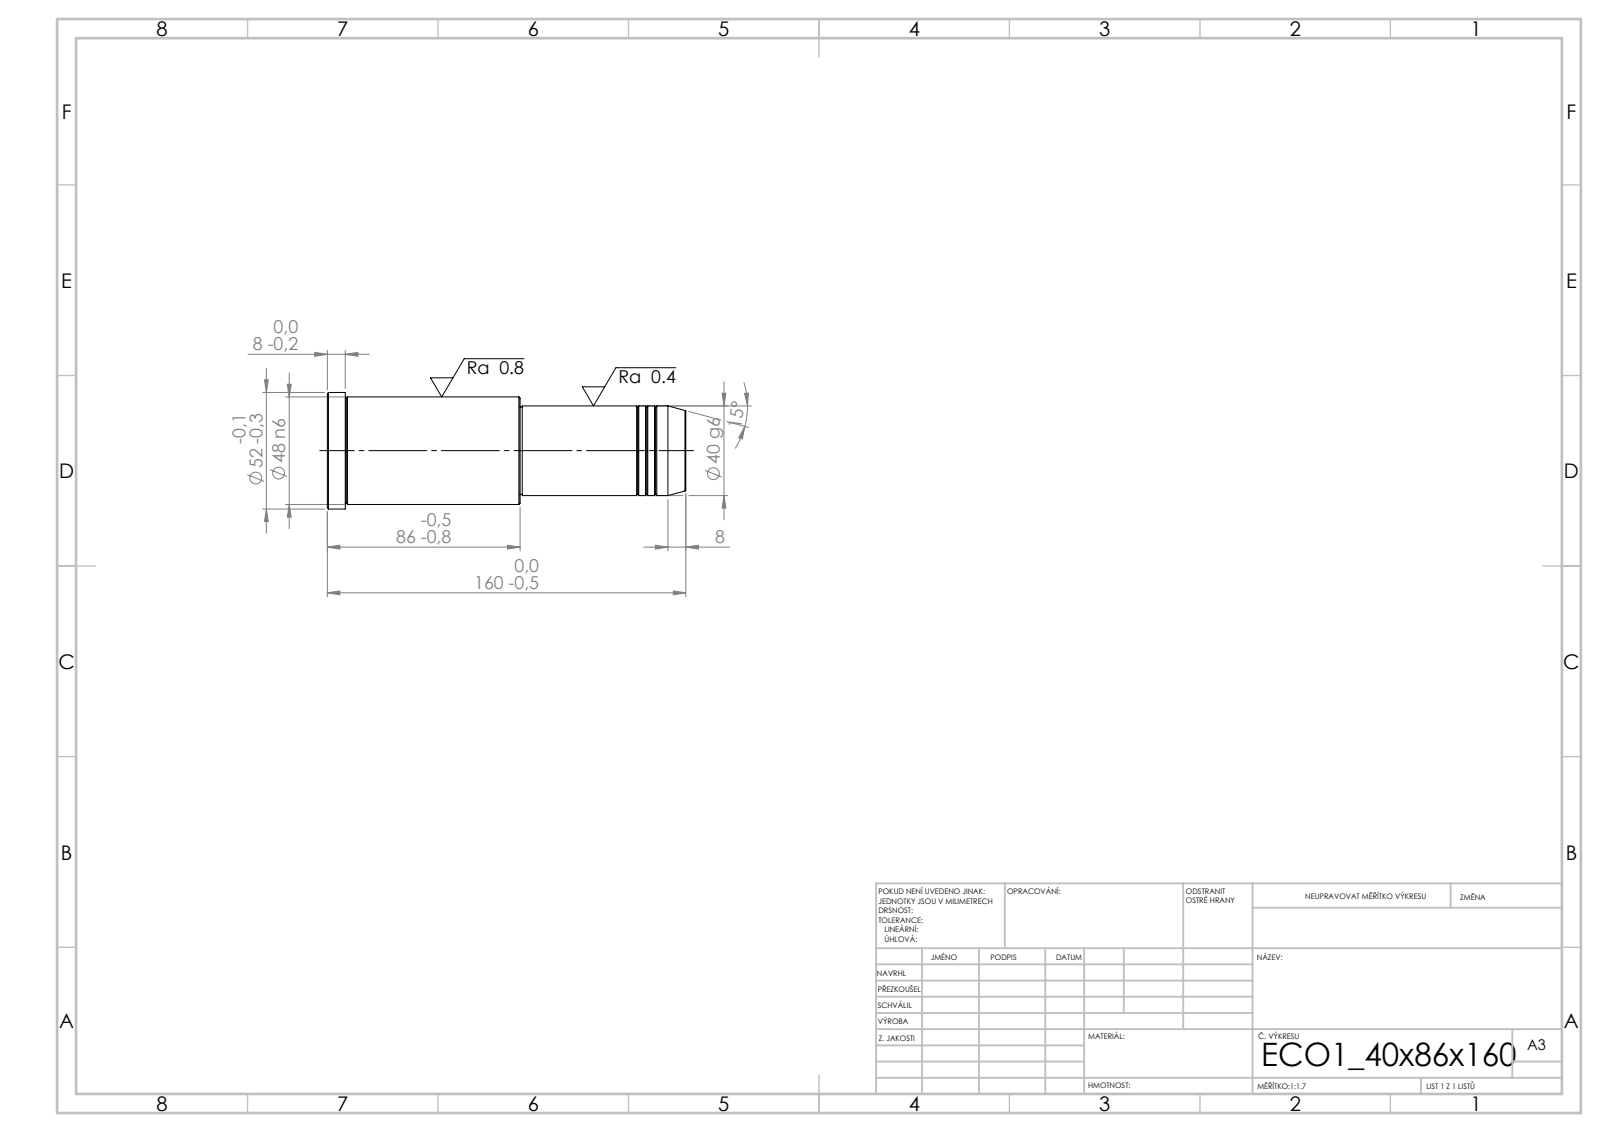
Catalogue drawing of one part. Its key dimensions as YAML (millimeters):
step_written_by: "SolidWorks 2019 (CONFIG_CONTROL_DESIGN)"
units: millimeters
bodies: {solids: 1, faces: 43, planar: 5, cylindrical: 14, other: 24}
overall_size: [160, 52, 52]
volume: 249778
surface_area: 26645
round_bosses_or_shafts:
  - {diameter: 52, count: 1}
  - {diameter: 48, count: 1}
  - {diameter: 40, count: 1}
  - {diameter: 39, count: 1}
face_to_face_distances: [160, 74, 86, 152, 78, 8, 73, 1, 79, 87]
